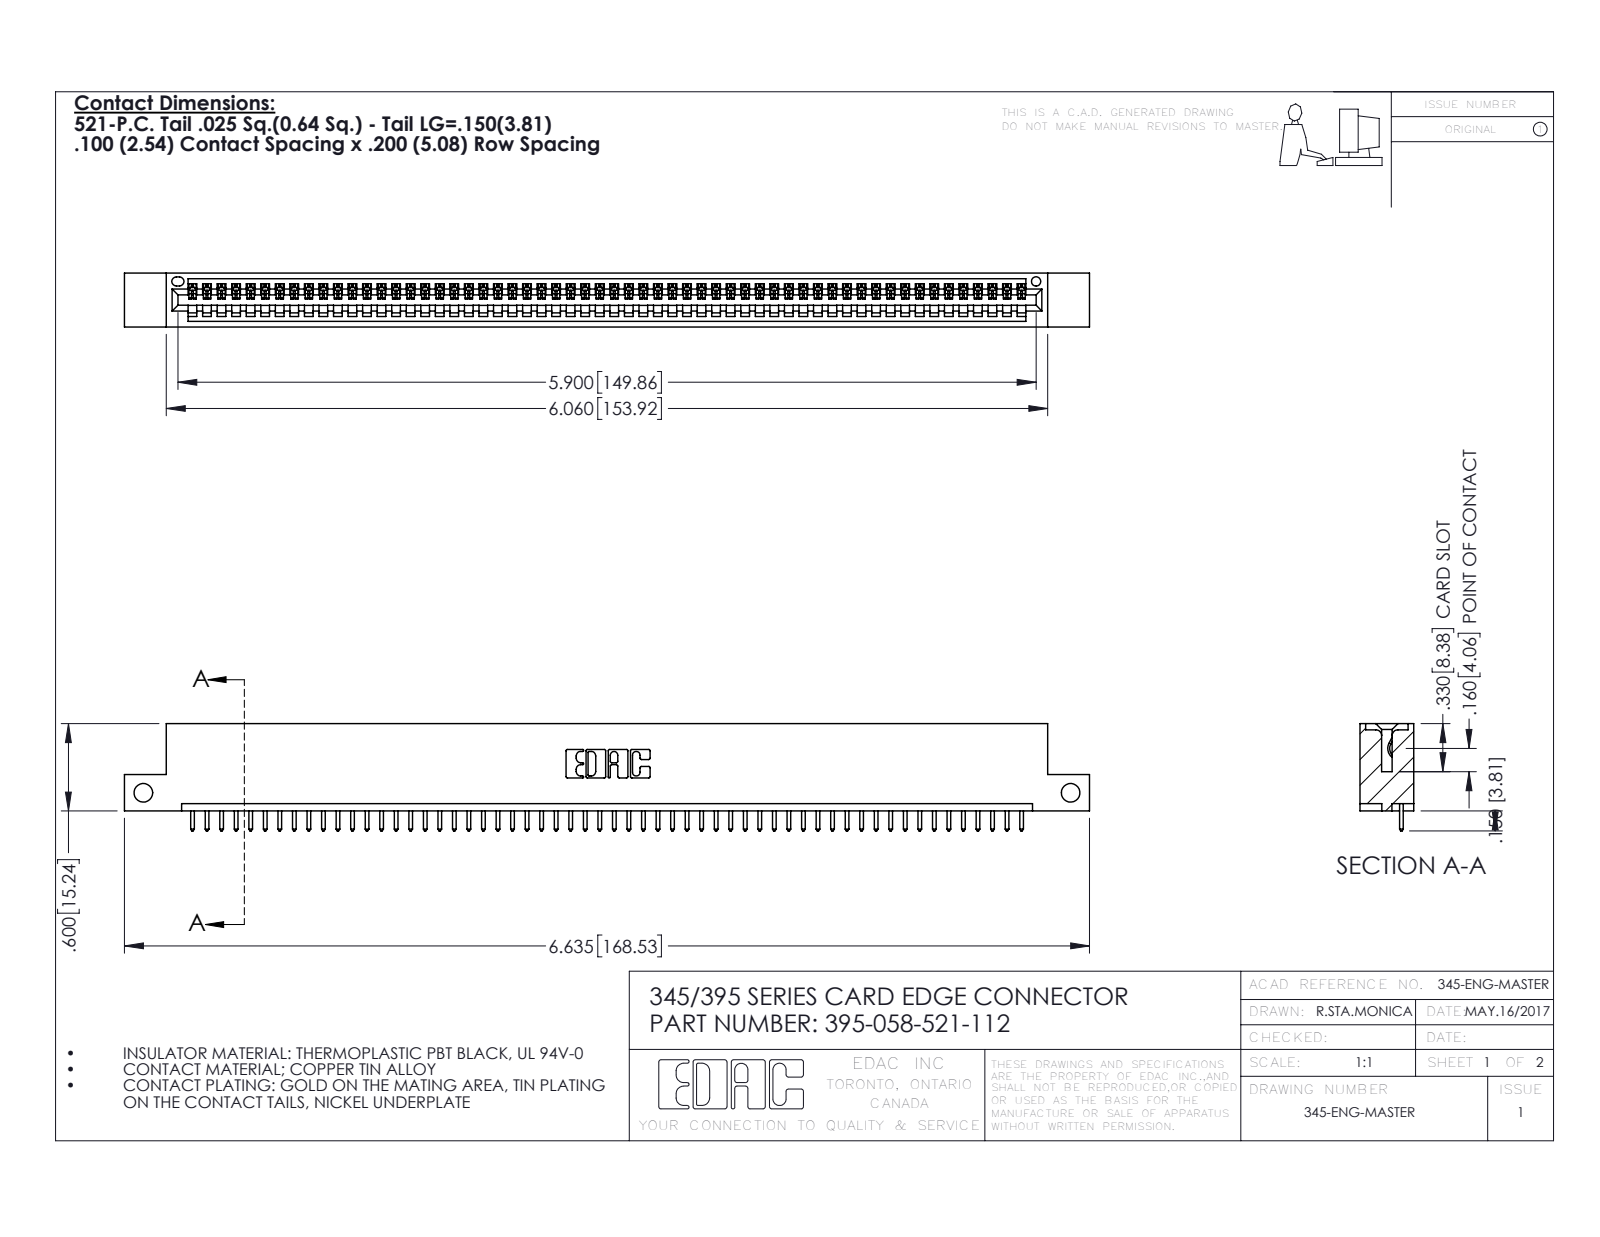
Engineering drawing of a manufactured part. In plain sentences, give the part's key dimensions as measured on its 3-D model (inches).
The part is named "345-292-001_345-293-121; 345 Part_Flush Mounting Lugs - Side Mount; 395-058-521-112". Its 3-D file was written by "SolidWorks 2016 (CONFIG_CONTROL_DESIGN)". It is 59 solids with 3490 faces: 2400 planar, 1090 cylindrical and 0 other. Overall it measures 6.635 by 0.737 by 0.37 inches. Its volume is 0.969 cubic inches and its surface area 31.84 square inches. Round holes: 2 of diameter 0.128, 1 of diameter 0.064. Partial cylindrical surfaces (rounded edges, fillets, slot ends): 116 of radius 0.006, 116 of radius 0.01, 22 of radius 0.01, 6 of radius 0.007, 6 of radius 0.031, 3 of radius 0.026, 2 of radius 0.031, 2 of radius 0.04. The main face-to-face distances are 0.298, 0.072, 0.37, 0.2, 0.098, 0.272, 0.025, 0.225, 0.149, 0.072. The hole center spacings are 6.375.
